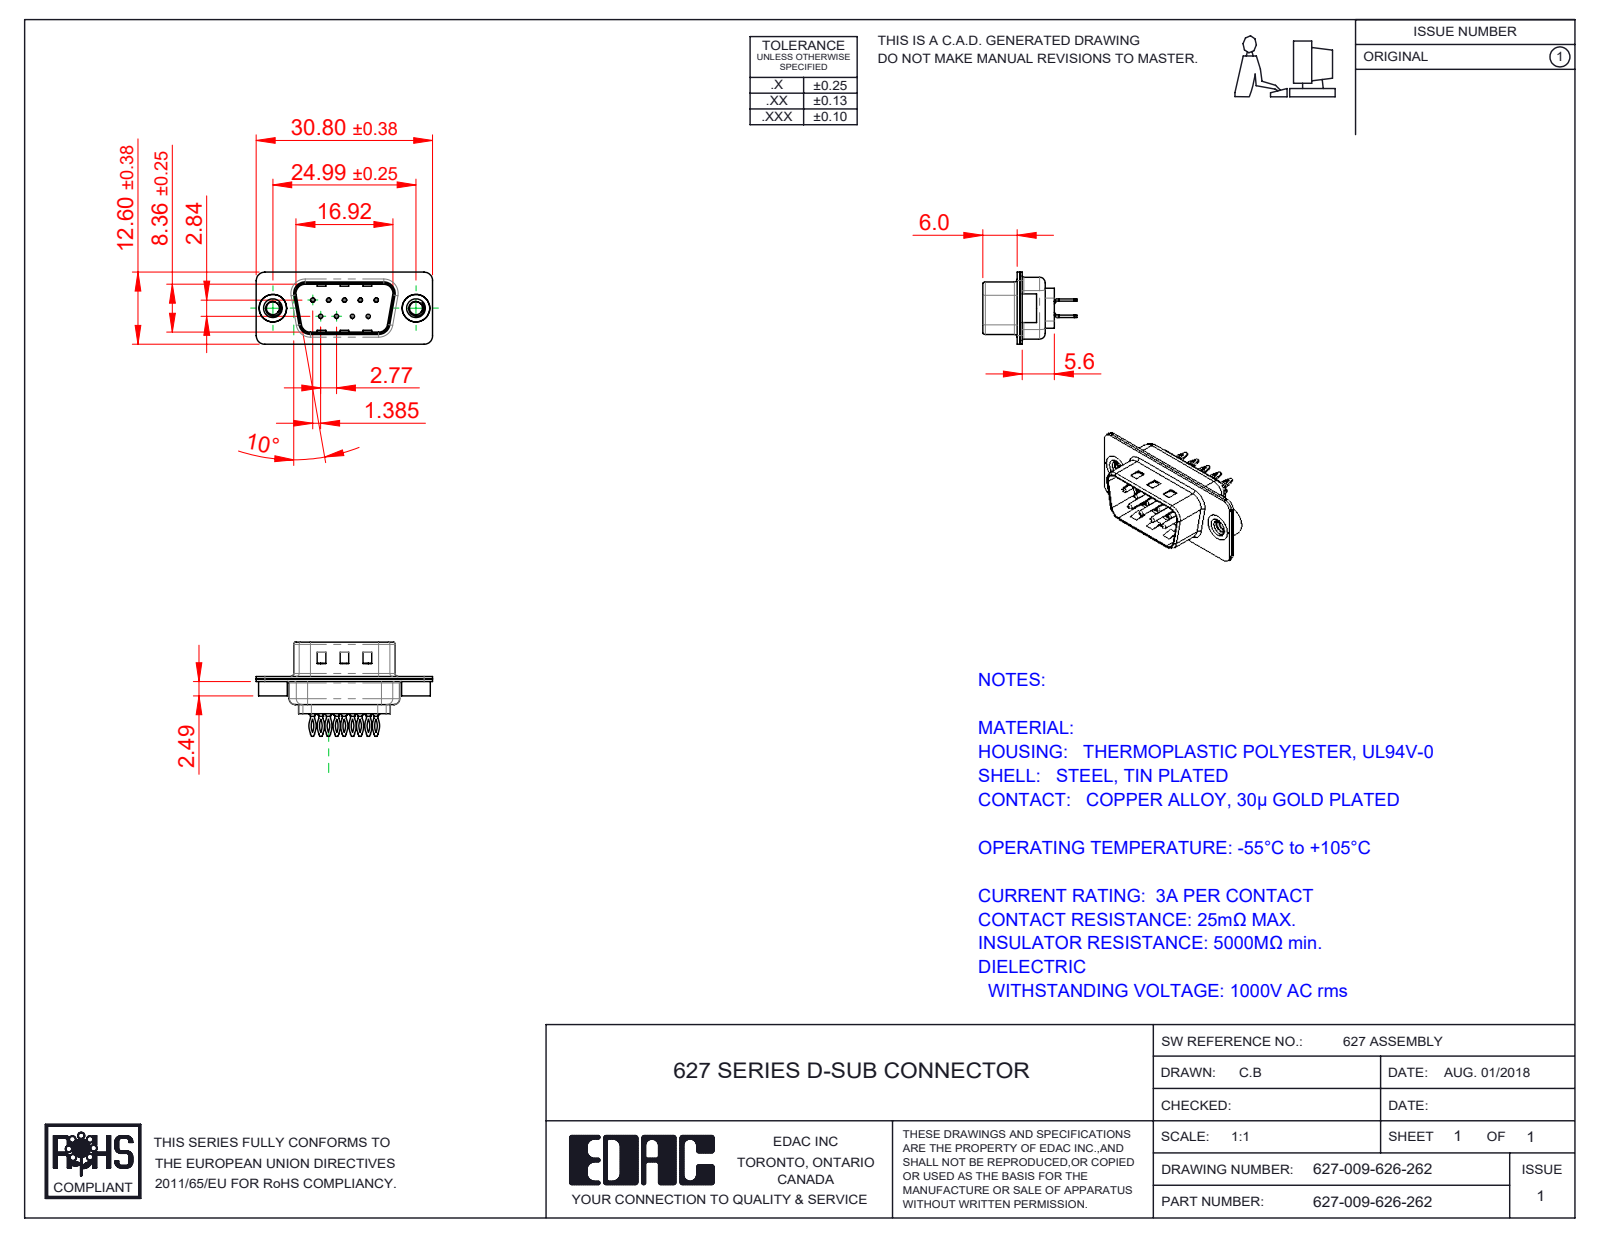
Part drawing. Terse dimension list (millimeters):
name: 627 Contact Row 2_26L; 627 Housing_09 LP; 627 Shell Rear_09 Contacts; 627 Contact Row 1_26L (+3 more)
written by: SolidWorks 2020 (CONFIG_CONTROL_DESIGN)
unit: mm
bodies: 14 solids, 984 faces (287 planar, 406 cylindrical, 291 other)
size: 30.8 × 16.45 × 12.6
volume: 1 307 mm³; area: 3 895 mm²
holes: 9× ⌀0.35, 9× ⌀1.1, 9× ⌀1.6, 2× ⌀2.26, 2× ⌀4, 2× ⌀4.8
bosses: 9× ⌀2, 9× ⌀1.5, 9× ⌀0.75, 2× ⌀5, 2× ⌀4.9
rounds: 18× R1.5, 18× R2.92, 18× R3.33, 12× R2, 8× R0.5, 8× R1.6, 4× R0.25, 4× R0.6
face distances: 0.4, 0.45, 0.9, 0.82, 9.58, 1.4, 8.76, 0.5, 1.5, 6.05
hole spacings: 3.16, 2.77, 5.54, 5.03, 5.04, 8.31, 7.48, 7.49
